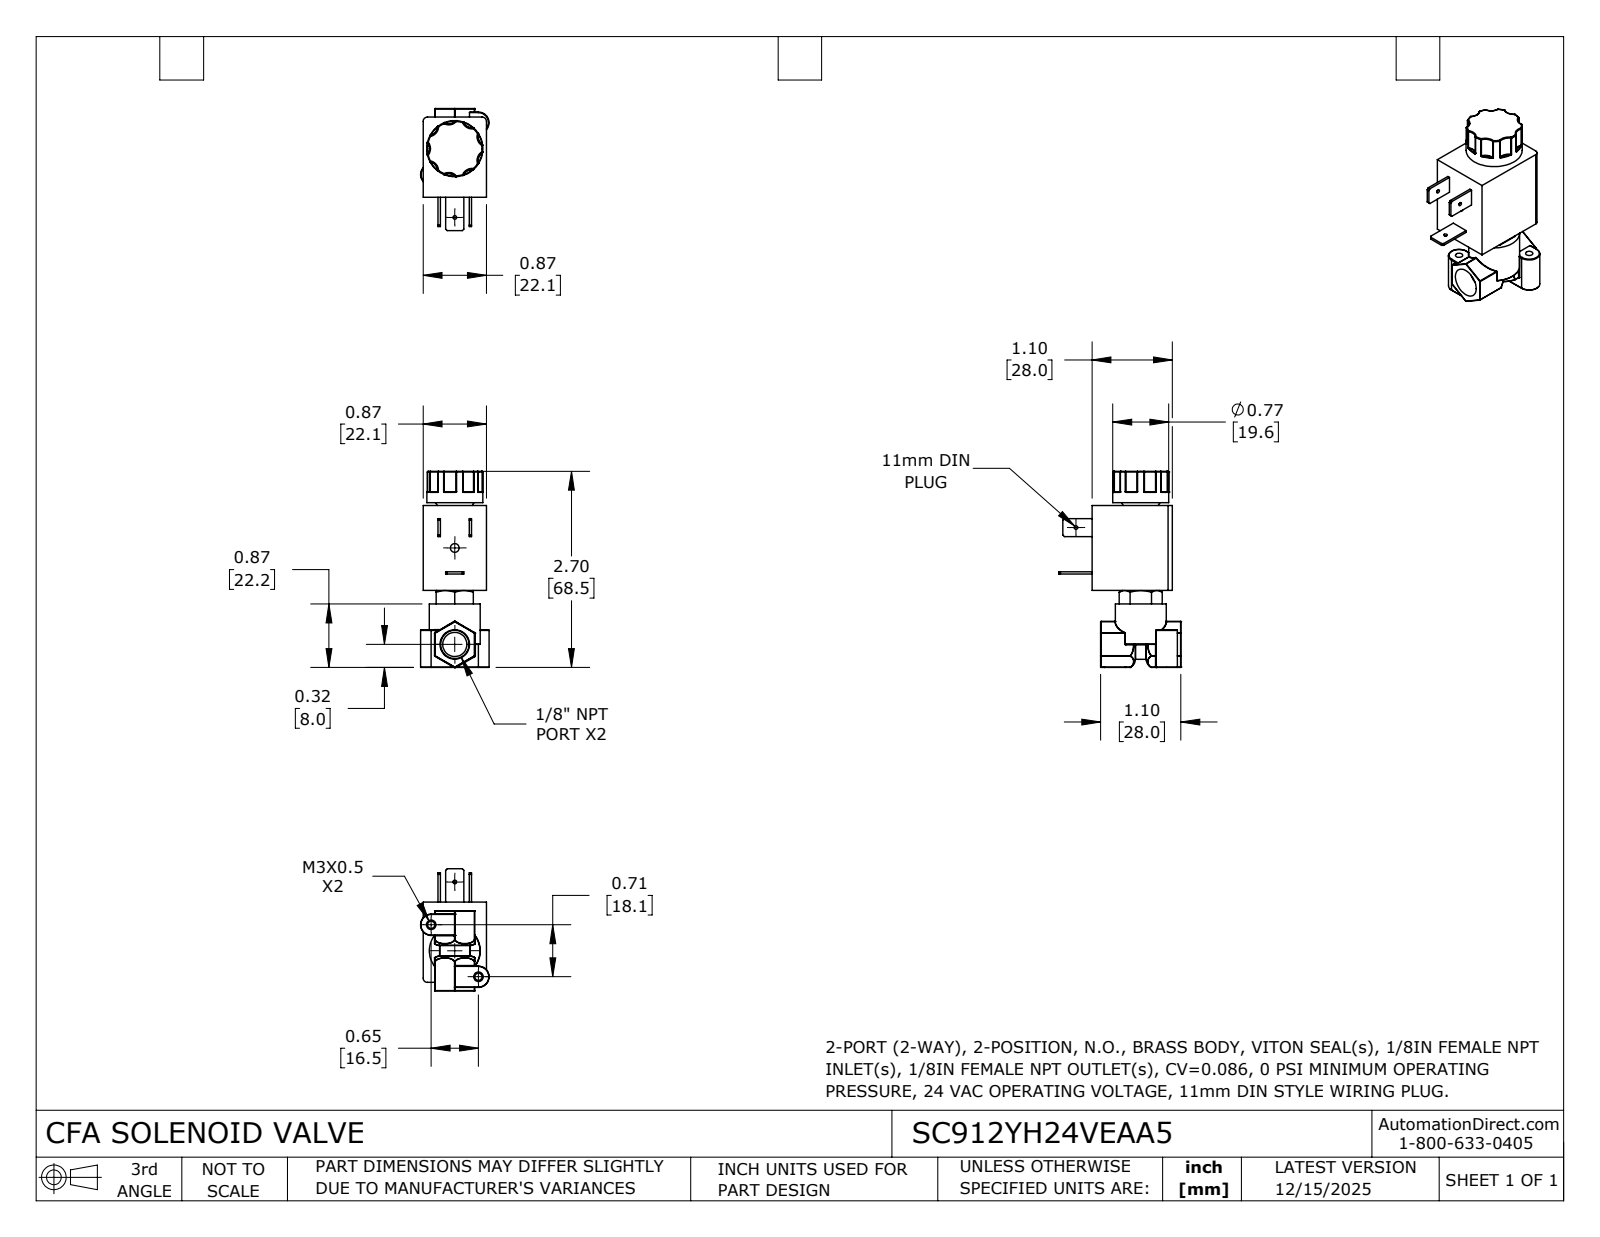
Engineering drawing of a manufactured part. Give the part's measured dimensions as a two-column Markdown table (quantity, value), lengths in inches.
| quantity | value |
| --- | --- |
| part name | SC912YH24VEAA5 |
| STEP written by | SolidWorks 2024 (CONFIG_CONTROL_DESIGN) |
| units | inches |
| bodies | 1 solid, 397 faces (76 planar, 110 cylindrical, 211 other) |
| overall size | 2.695 × 1.678 × 0.942 |
| volume | 1.739 in³ |
| surface area | 14.05 in² |
| round holes (diameter × count) | 0.05 × 2, 0.1 × 2, 0.12 × 1, 0.332 × 1 |
| round bosses / shafts (diameter × count) | 0.77 × 1, 0.7 × 1 |
| partial cylindrical surfaces (radius × count) | 0.004 × 29, 0.01 × 18, 0.008 × 12, 0.133 × 7, 0.017 × 2, 0.06 × 2, 0.132 × 2, 0.146 × 2 |
| main face-to-face distances | 0.87, 1.104, 1.167, 1.637, 0.47, 0.548, 0.031, 0.161, 0.709, 1.207 |
| hole center spacings | 0.672, 0.965, 1.326, 1.342 |
